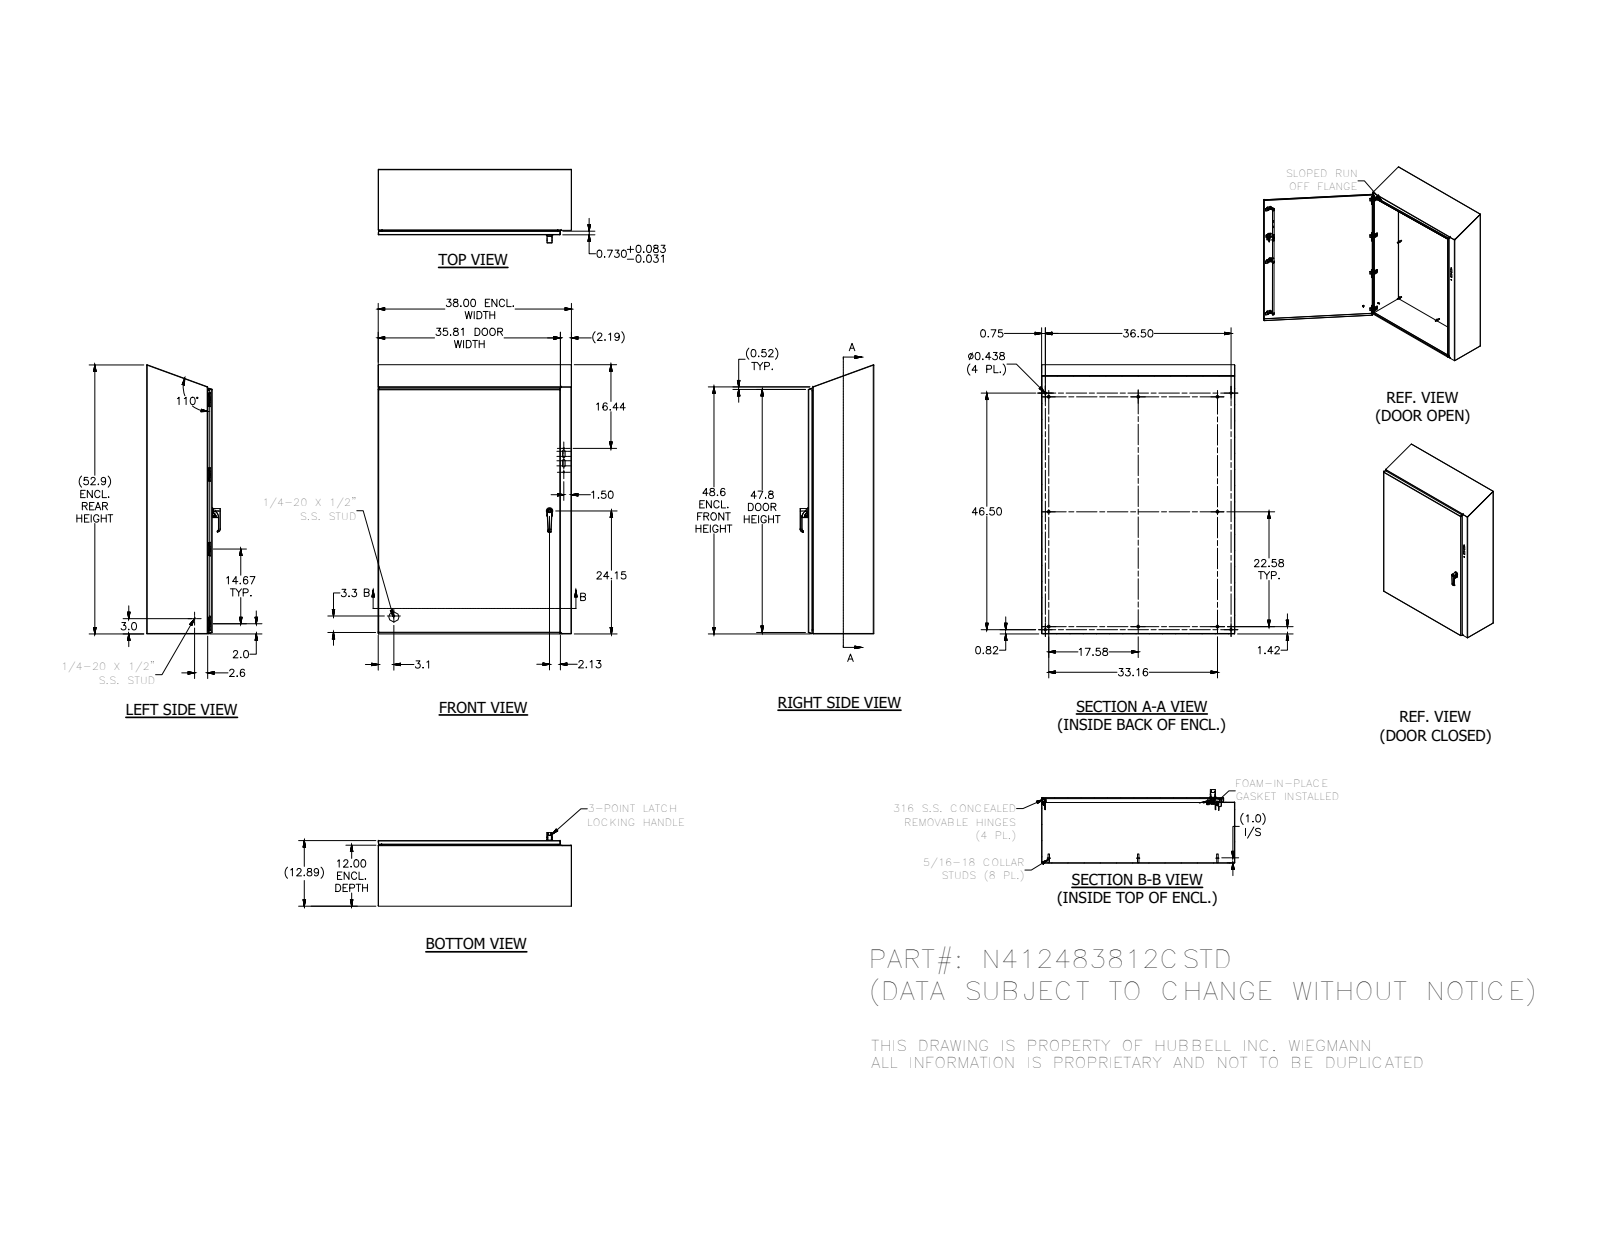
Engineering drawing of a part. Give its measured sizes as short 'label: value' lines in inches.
name: N412483812CSTDBLR; 388150; N4123812CSTDTOP; 38846 (+8 more)
written by: Autodesk Inventor 2014 (AUTOMOTIVE_DESIGN)
unit: in
bodies: 93 solids, 3129 faces (1174 planar, 1143 cylindrical, 812 other)
size: 52.896 × 38 × 14.481
volume: 479.5 in³; area: 12 890 in²
holes: 8× ⌀0.093, 8× ⌀0.152, 8× ⌀0.167, 8× ⌀0.172, 8× ⌀0.187, 7× ⌀0.156, 6× ⌀0.145, 4× ⌀0.32, 4× ⌀0.437, 3× ⌀0.196, 3× ⌀0.211, 3× ⌀0.22
bosses: 20× ⌀0.25, 14× ⌀0.3, 8× ⌀0.563, 8× ⌀0.36, 8× ⌀0.32, 8× ⌀0.275, 8× ⌀0.256, 8× ⌀0.164
rounds: 50× R0.05, 45× R0.125, 38× R0.02, 36× R0.031, 34× R0.016, 30× R0.012, 24× R0.025, 18× R0.105
face distances: 0.074, 12.813, 12.739, 12.887, 37.926, 38, 37.852, 11.926, 0.887, 0.813
hole spacings: 14.667, 14.667, 29.333, 44, 20.687, 29.333, 0.5, 0.656
